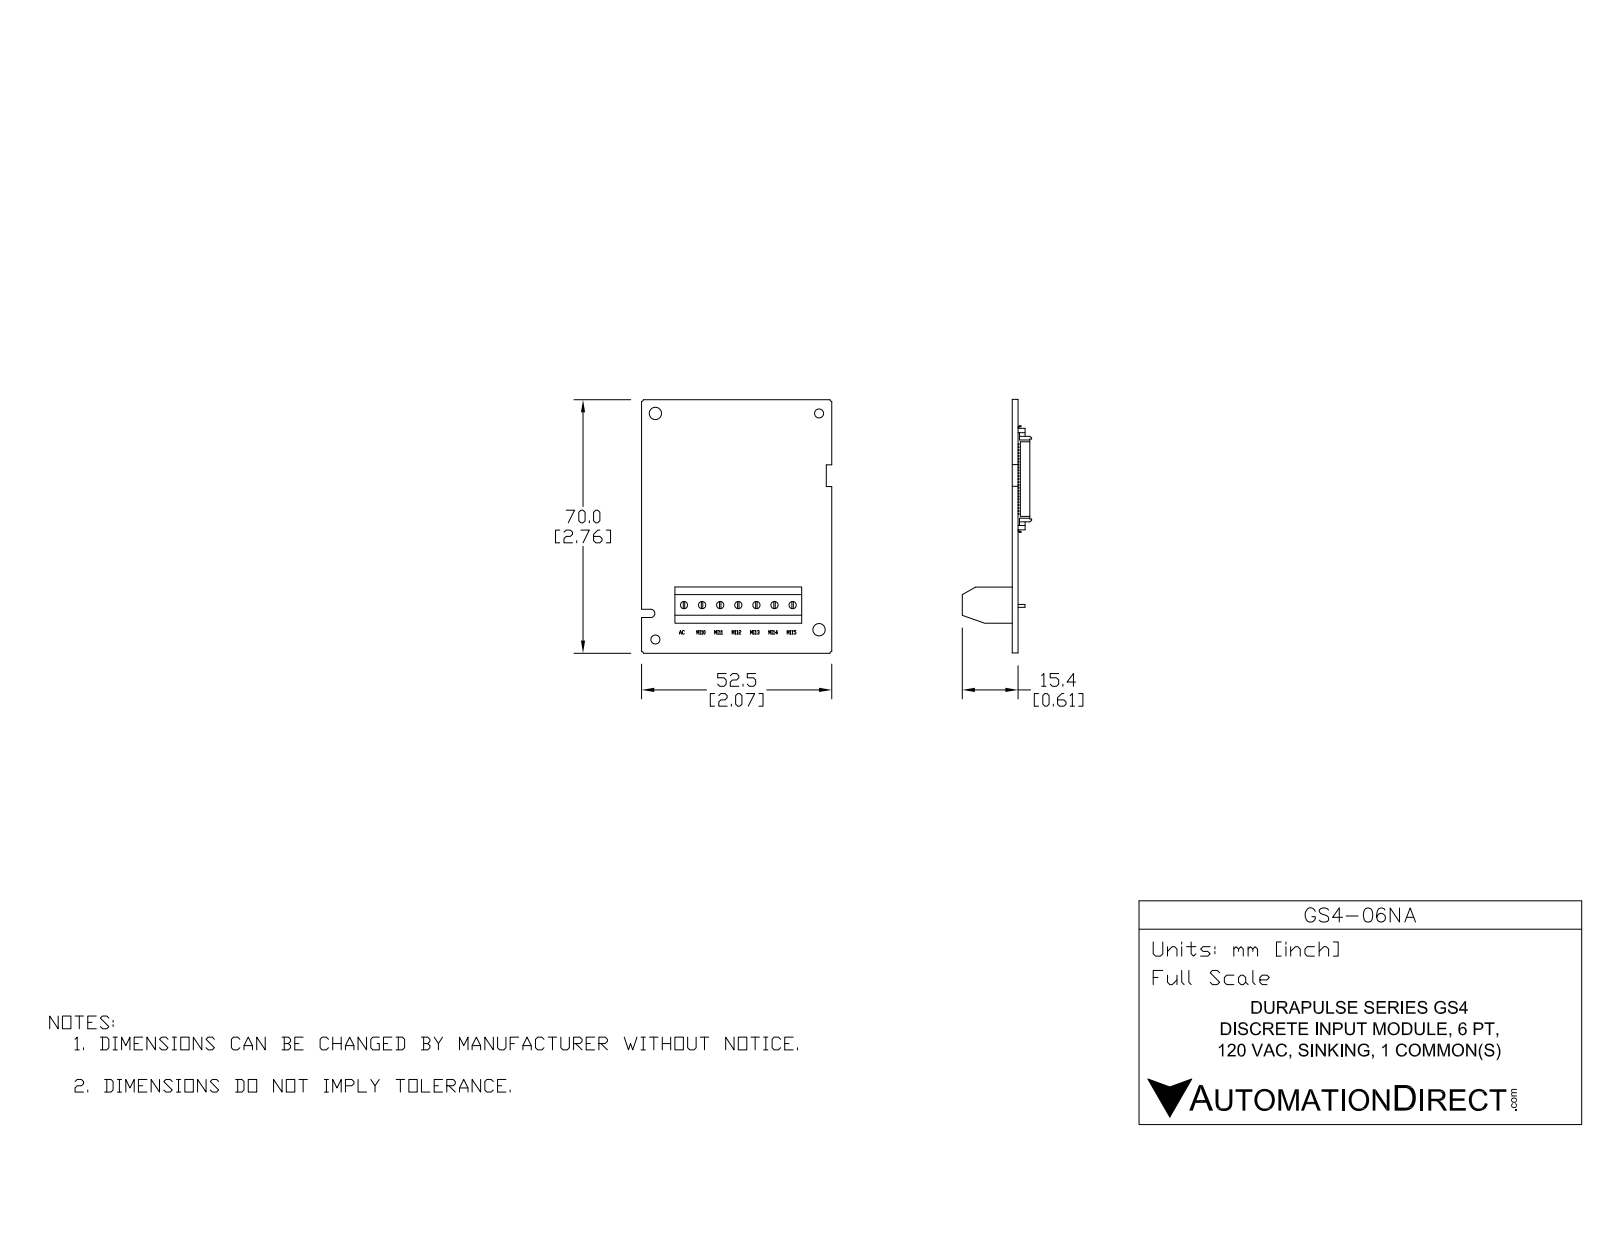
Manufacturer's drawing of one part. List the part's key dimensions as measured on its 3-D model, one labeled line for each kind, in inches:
Part name (STEP PRODUCT): GS4-06NA
STEP written by: SolidWorks 2016 (AUTOMOTIVE_DESIGN)
Units: inches
Bodies: 3 solids, 645 faces (582 planar, 59 cylindrical, 4 other)
Overall size (bounding box): 2.756 × 2.067 × 0.754
Volume: 0.617 in³ · Surface area: 16.37 in²
Round holes (diameter × count): ⌀0.039 ×9, ⌀0.079 ×7, ⌀0.098 ×2, ⌀0.134 ×2, ⌀0.031 ×1
Partial cylindrical surfaces — rounded edges, fillets, slot ends (radius × count): R0.01 ×4, R0.02 ×4, R0.045 ×1
Main face-to-face distances: 0.063, 0.079, 0.327, 0.02, 0.606, 0.543, 0.394, 0.315, 0.138, 1.378
Hole centre spacings: 0.197, 0.394, 0.1, 0.591, 0.787, 0.984, 1.624, 1.801
